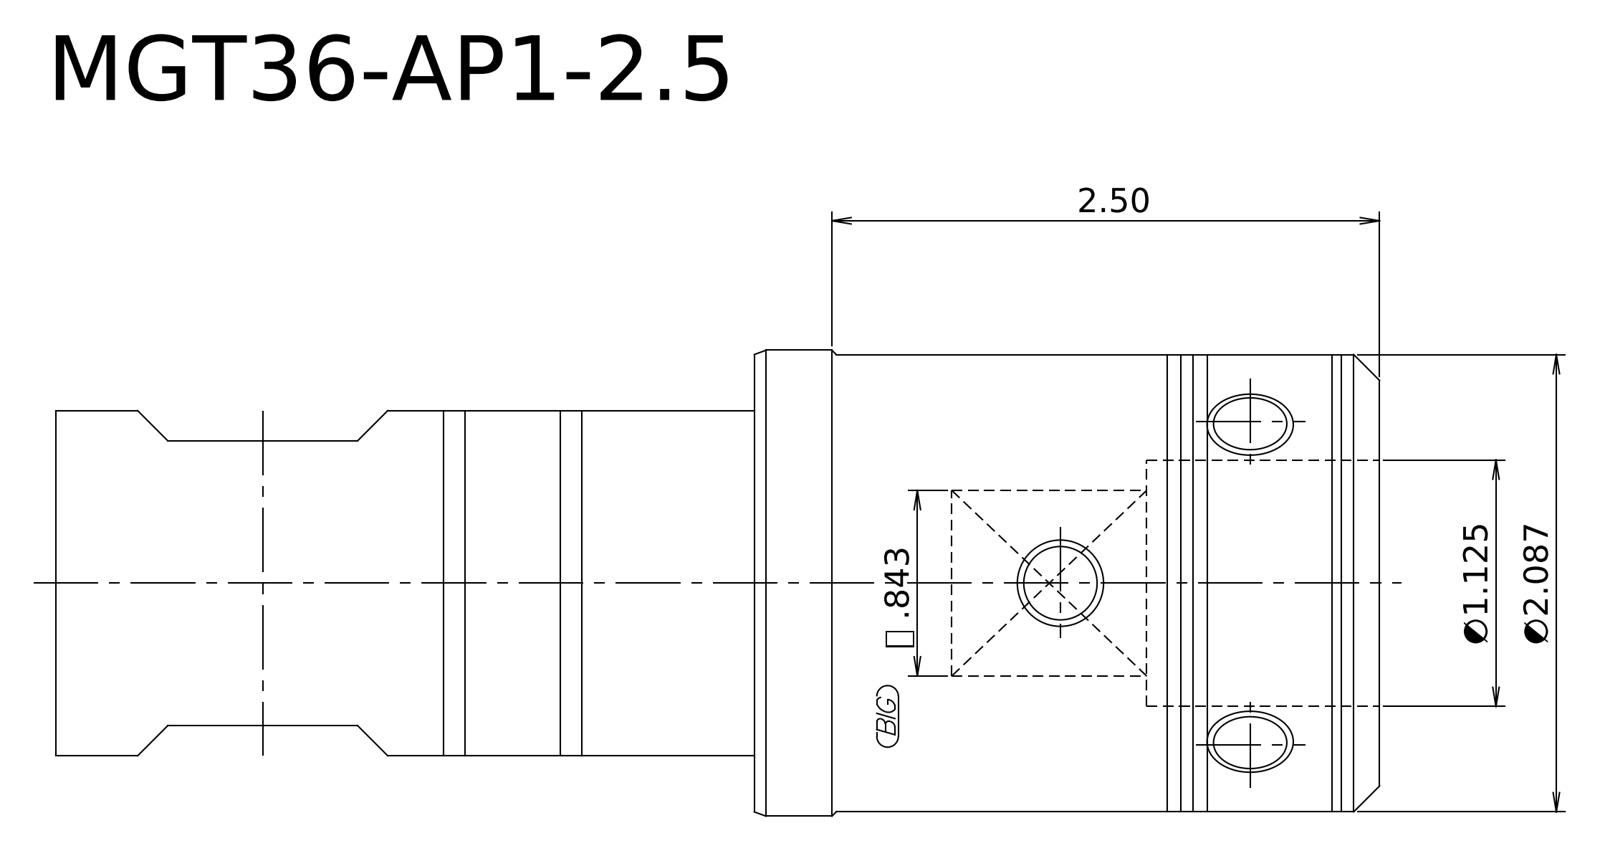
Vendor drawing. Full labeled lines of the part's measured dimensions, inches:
STEP written by: Kubotek KeyCreator 2011 V10.0.2 (22737) (automotive_design)
Units: inches
Bodies: 1 solid, 9 faces (3 planar, 3 cylindrical, 3 other)
Overall size (bounding box): 6.043 × 2.126 × 2.126
Volume: 15.97 in³ · Surface area: 40.97 in²
Round bosses / shafts (diameter × count): ⌀2.126 ×1, ⌀2.087 ×1, ⌀1.575 ×1
Main face-to-face distances: 6.043, 2.854, 3.189
